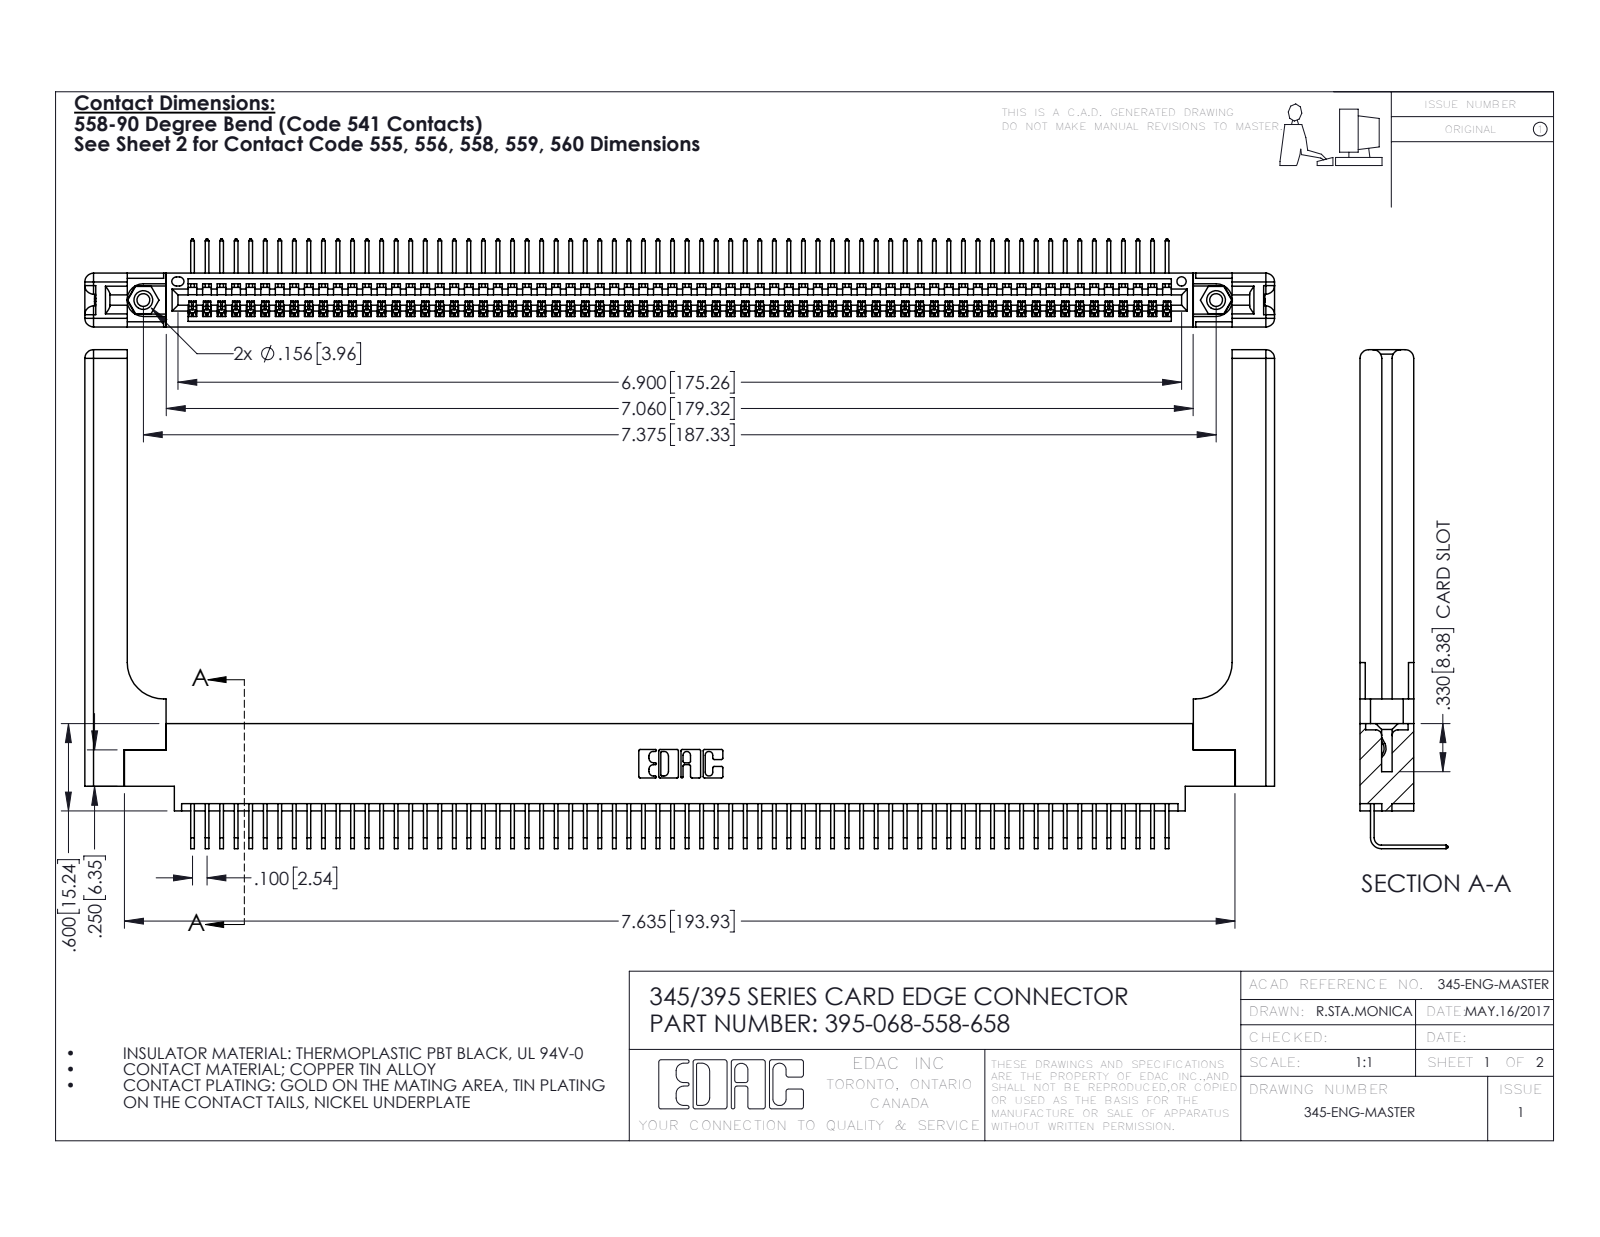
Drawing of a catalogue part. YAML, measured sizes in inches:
part_name: "345 Part_0.170 Offset - 0.156 Dia-TH; 345-250-001_345-250-001-102; 345-220-058_345-220-058; 345-292-001_558 Tail - 2 (+1 more)"
step_written_by: "SolidWorks 2016 (CONFIG_CONTROL_DESIGN)"
units: inches
bodies: {solids: 73, faces: 4466, planar: 3088, cylindrical: 1318, other: 60}
overall_size: [8.179, 3.429, 0.605]
volume: 1.743
surface_area: 52.35
round_holes:
  - {diameter: 0.089, count: 2}
  - {diameter: 0.125, count: 2}
  - {diameter: 0.156, count: 2}
  - {diameter: 0.064, count: 1}
round_bosses_or_shafts:
  - {diameter: 0.155, count: 2}
partial_cylinders:
  - {radius: 0.006, count: 136}
  - {radius: 0.01, count: 22}
  - {radius: 0.06, count: 16}
  - {radius: 0.007, count: 6}
  - {radius: 0.031, count: 6}
  - {radius: 0.026, count: 3}
  - {radius: 0.03, count: 2}
  - {radius: 0.031, count: 2}
face_to_face_distances: [0.072, 0.37, 0.298, 0.098, 0.272, 0.025, 0.2, 0.225, 0.148, 0.15]
hole_center_spacings: [0.27, 7.139, 7.375]
